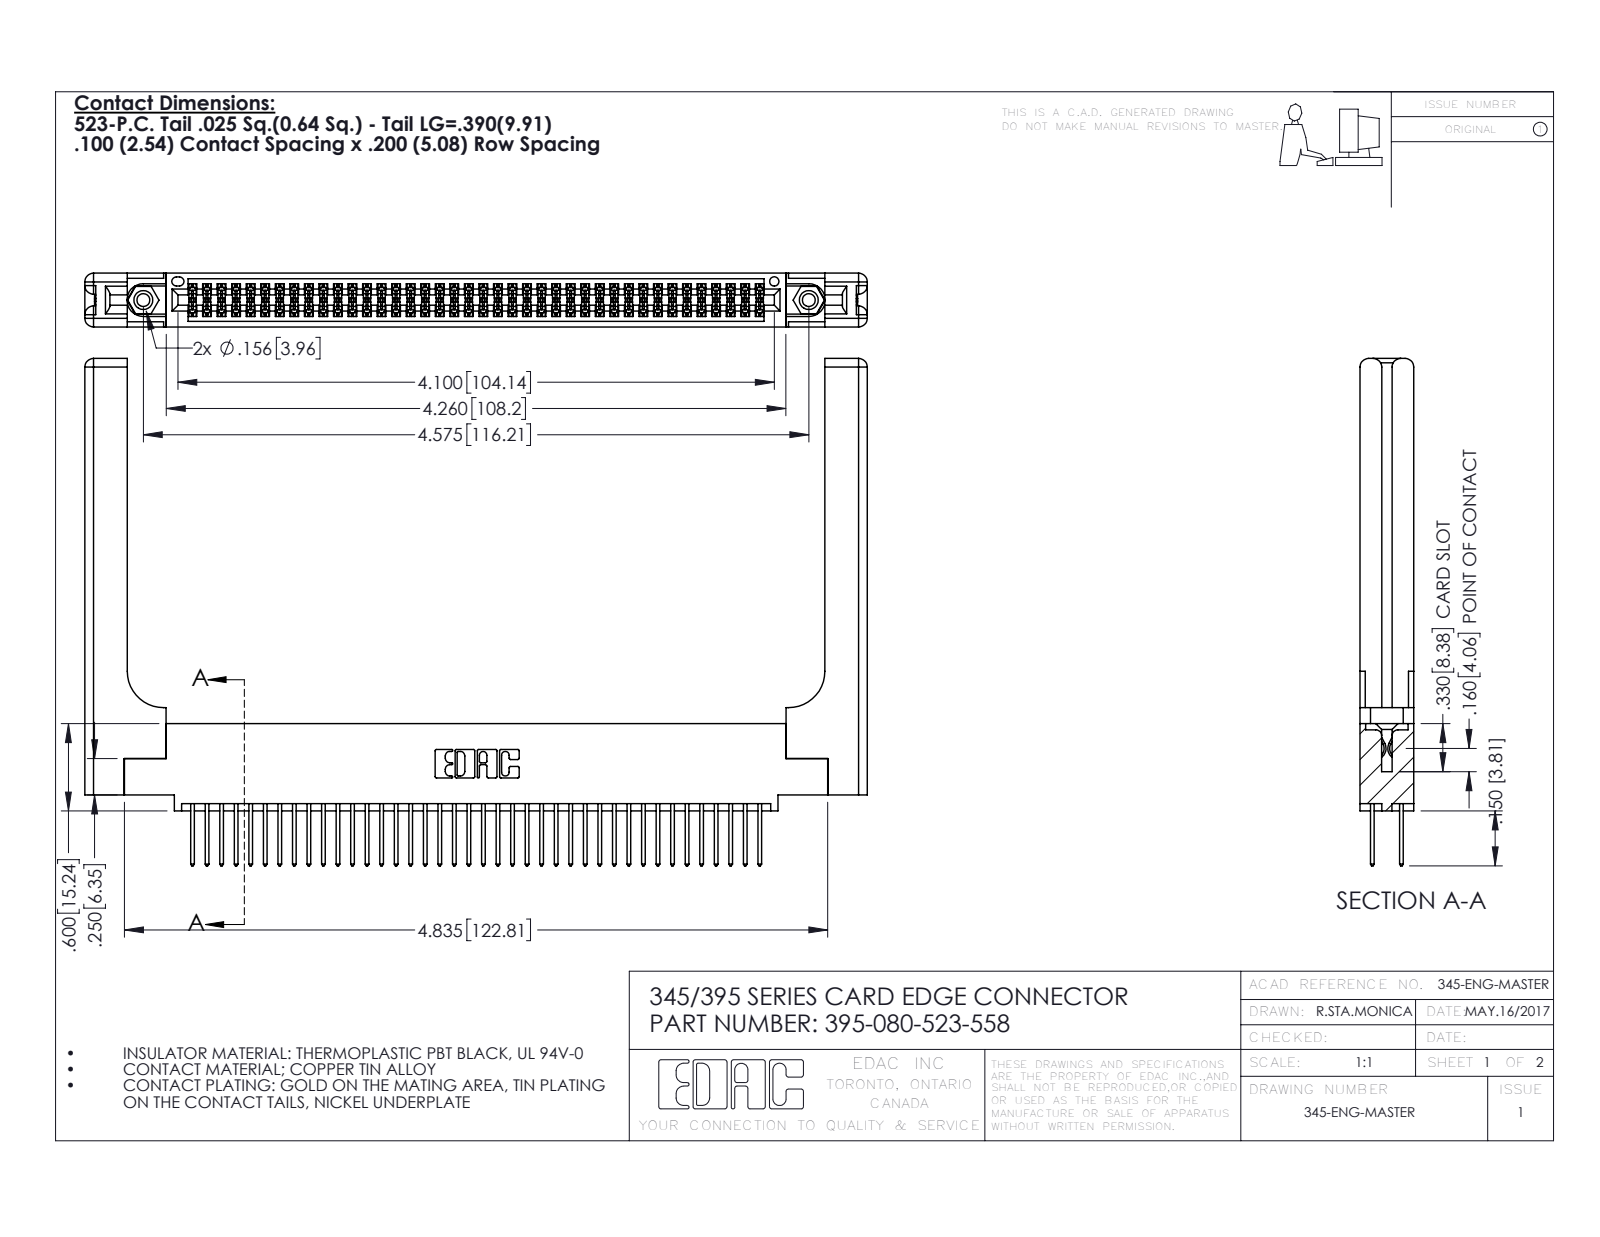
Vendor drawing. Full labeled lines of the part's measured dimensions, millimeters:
Part name (STEP PRODUCT): 345 Part_0.110 Offset - 0.156 Dia-TH; 395-080-523-558; 345-292-001_345-293-123; 345-220-058_345-220-058 (+1 more)
STEP written by: SolidWorks 2016 (CONFIG_CONTROL_DESIGN)
Units: millimetres
Bodies: 85 solids, 4386 faces (2872 planar, 1454 cylindrical, 60 other)
Overall size (bounding box): 136.6 × 88.6 × 9.4
Volume: 21 810 mm³ · Surface area: 25 570 mm²
Round holes (diameter × count): ⌀2.3 ×2, ⌀3.2 ×2, ⌀4 ×2, ⌀1.6 ×1
Round bosses / shafts (diameter × count): ⌀3.9 ×2
Partial cylindrical surfaces — rounded edges, fillets, slot ends (radius × count): R0.2 ×120, R0.3 ×80, R0.3 ×22, R1.5 ×16, R0.2 ×6, R0.8 ×6, R0.7 ×3, R0.4 ×2
Main face-to-face distances: 1.8, 7.6, 9.4, 2.5, 6.9, 0.6, 5.1, 5.7, 3.8, 3.8
Hole centre spacings: 6.9, 110.2, 116.2
